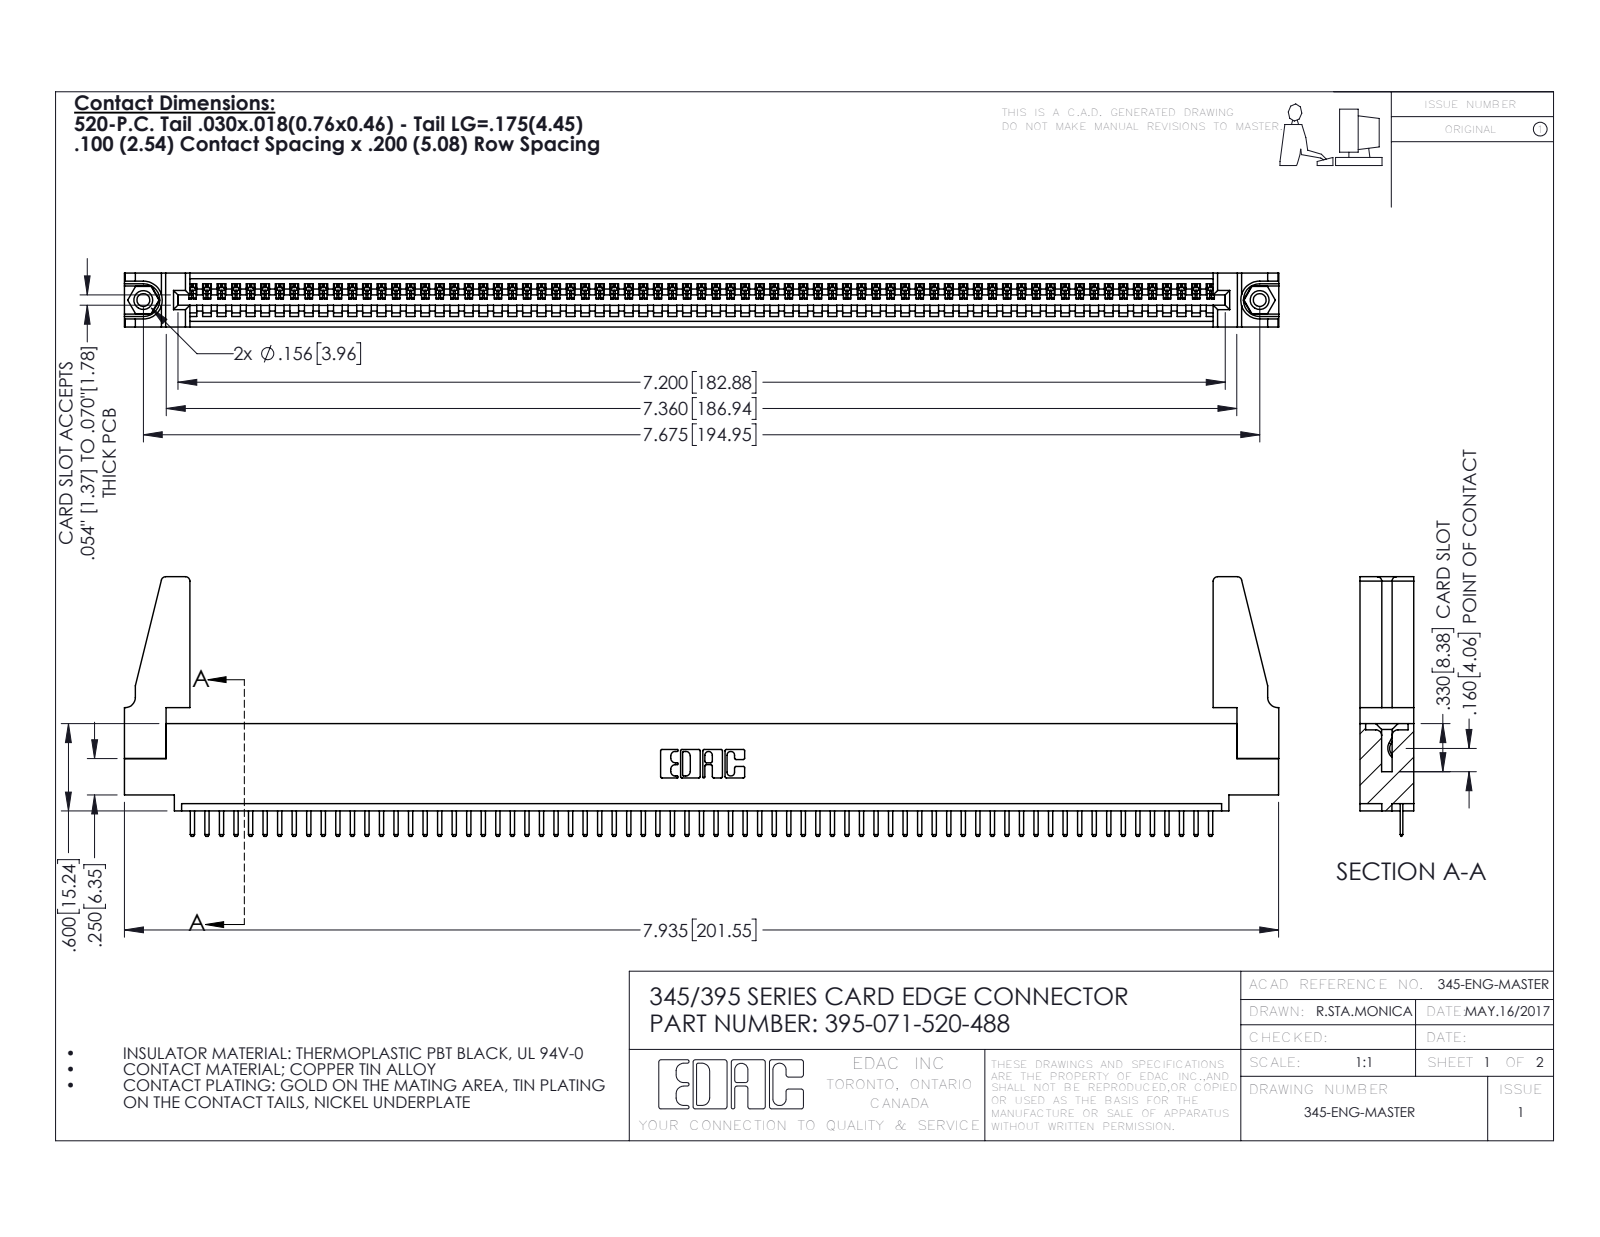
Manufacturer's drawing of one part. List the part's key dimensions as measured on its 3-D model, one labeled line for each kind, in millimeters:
Part name (STEP PRODUCT): 345-250-001_345-250-001-102; 345-292-001_345-293-120; 345-220-078_345-220-088; 345 Part_0.110 Offset - 0.156 Dia-TH (+1 more)
STEP written by: SolidWorks 2016 (CONFIG_CONTROL_DESIGN)
Units: millimetres
Bodies: 76 solids, 4656 faces (3138 planar, 1502 cylindrical, 16 other)
Overall size (bounding box): 201.6 × 45.3 × 9.4
Volume: 22 350 mm³ · Surface area: 28 330 mm²
Round holes (diameter × count): ⌀2.3 ×2, ⌀3.2 ×2, ⌀4 ×2, ⌀1.6 ×1
Round bosses / shafts (diameter × count): ⌀3.9 ×2
Partial cylindrical surfaces — rounded edges, fillets, slot ends (radius × count): R0.3 ×144, R0.2 ×142, R0.3 ×22, R0.8 ×8, R0.2 ×6, R0.8 ×6, R0.7 ×3, R0.8 ×2
Main face-to-face distances: 1.8, 7.6, 9.4, 2.5, 6.9, 0.6, 5.1, 5.7, 1.8, 3.8
Hole centre spacings: 6.9, 189, 194.9
